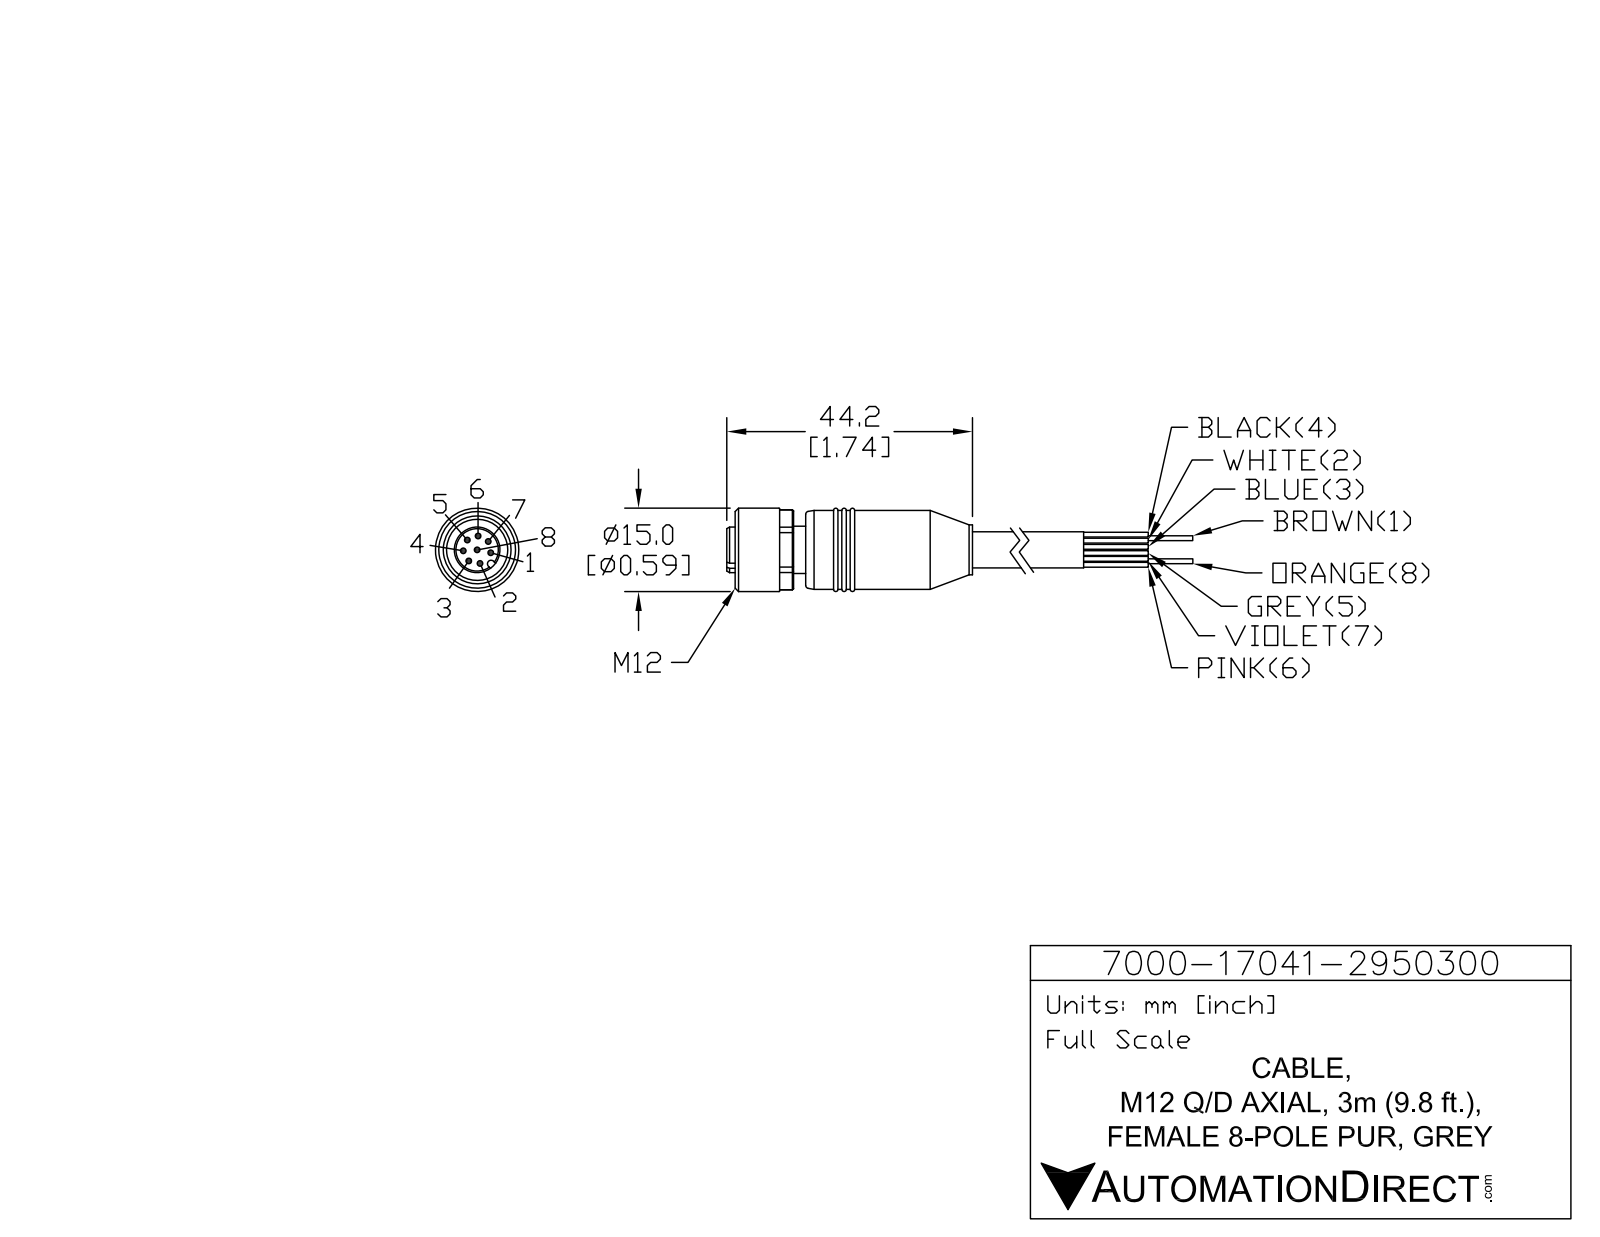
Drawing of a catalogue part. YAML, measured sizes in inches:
part_name: "7000-17041-2950300"
step_written_by: "SolidWorks 2015 (AUTOMOTIVE_DESIGN)"
units: inches
bodies: {solids: 1, faces: 103, planar: 31, cylindrical: 44, other: 28}
overall_size: [2.528, 0.591, 0.591]
volume: 0.404
surface_area: 5.259
round_holes:
  - {diameter: 0.039, count: 8}
  - {diameter: 0.433, count: 1}
round_bosses_or_shafts:
  - {diameter: 0.591, count: 1}
  - {diameter: 0.559, count: 1}
  - {diameter: 0.354, count: 1}
  - {diameter: 0.335, count: 1}
  - {diameter: 0.323, count: 1}
  - {diameter: 0.256, count: 1}
partial_cylinders:
  - {radius: 0.026, count: 1}
  - {radius: 0.283, count: 1}
face_to_face_distances: [0.087, 0.512, 0.118, 0.205, 0.354, 0.472, 0.559, 2.528, 2.173, 2.055]
hole_center_spacings: [0.098, 0.081, 0.149, 0.195, 0.082, 0.166, 0.189, 0.189]
